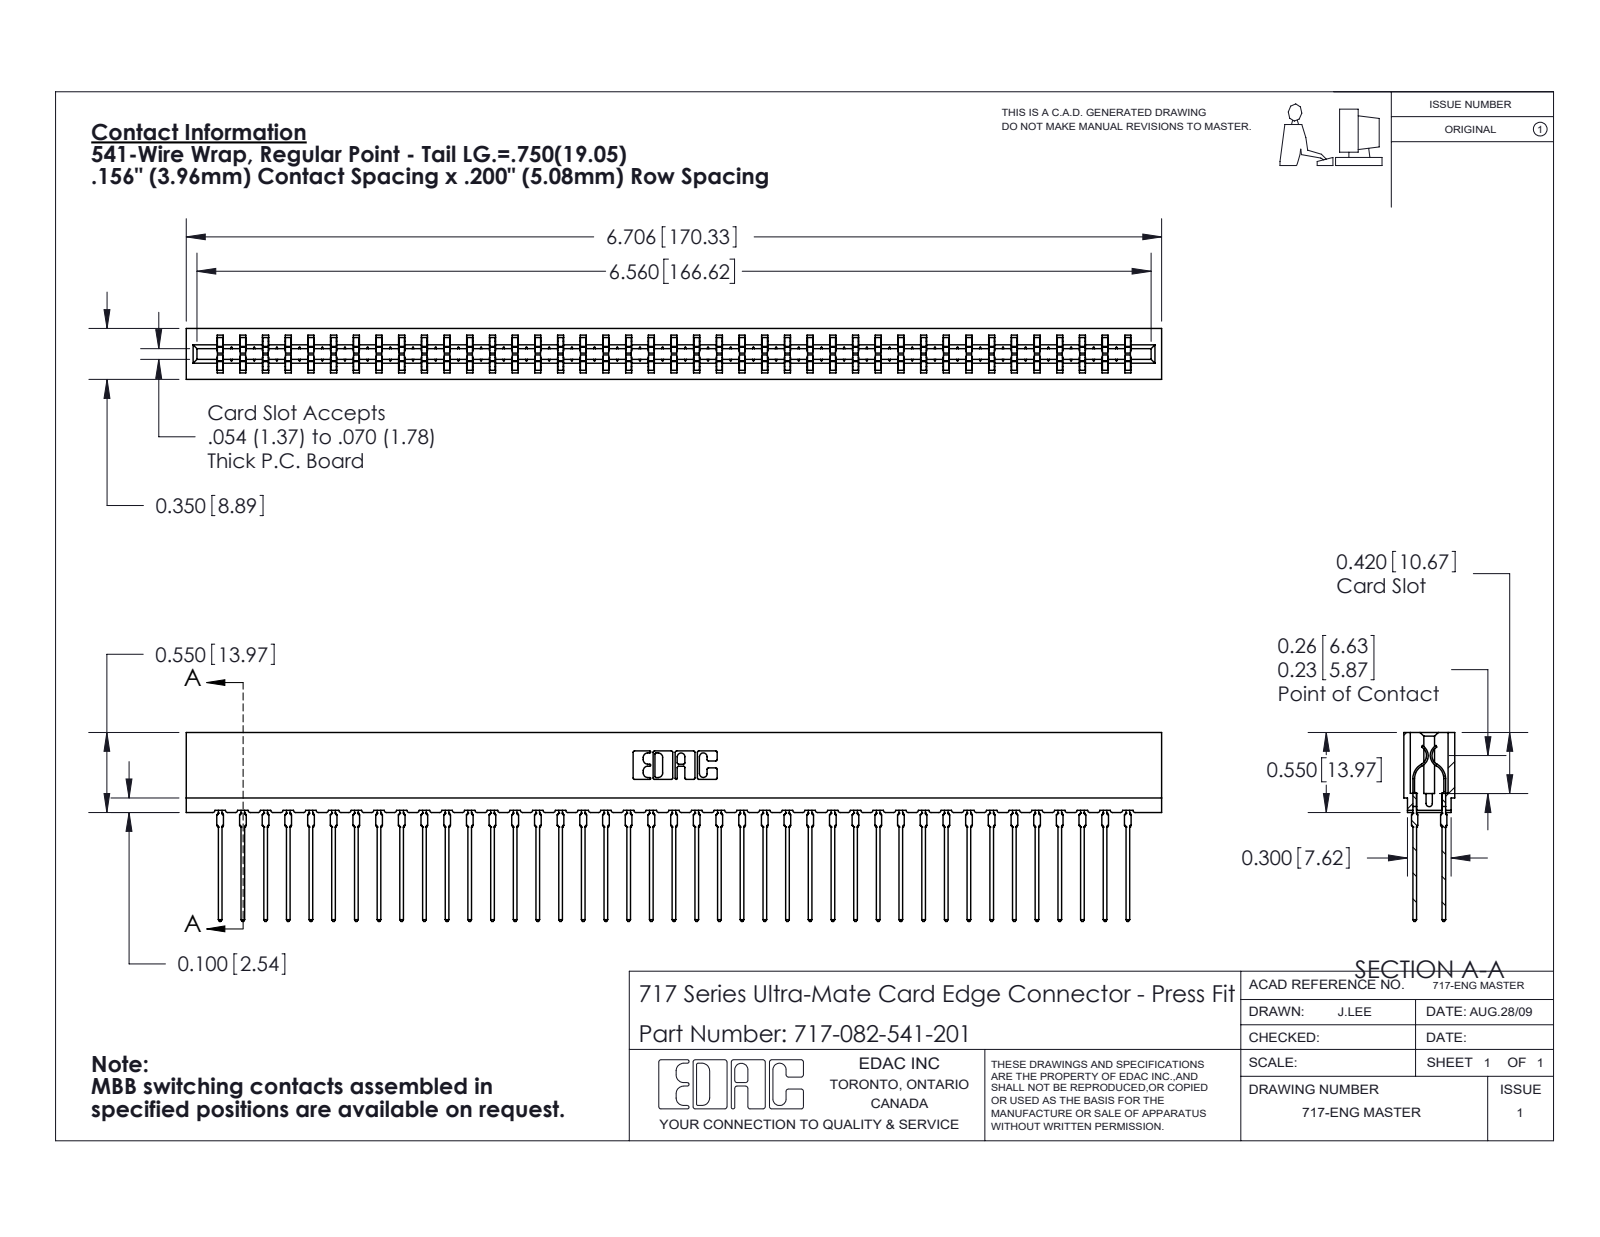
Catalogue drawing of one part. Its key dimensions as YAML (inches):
part_name: "745-292-001_541; 717 Part_Insulator Option - 06; 717-082-541-201"
step_written_by: "SolidWorks 2020 (CONFIG_CONTROL_DESIGN)"
units: inches
bodies: {solids: 83, faces: 7474, planar: 3867, cylindrical: 1475, other: 2132}
overall_size: [6.706, 1.299, 0.35]
volume: 0.925
surface_area: 38.77
partial_cylinders:
  - {radius: 0.021, count: 164}
  - {radius: 0.015, count: 82}
  - {radius: 0.01, count: 22}
  - {radius: 0.005, count: 8}
  - {radius: 0.011, count: 8}
  - {radius: 0.007, count: 6}
  - {radius: 0.031, count: 6}
  - {radius: 0.026, count: 3}
face_to_face_distances: [0.212, 0.138, 0.35, 0.063, 0.287, 0.076, 0.149, 0.087, 0.263, 0.025]
